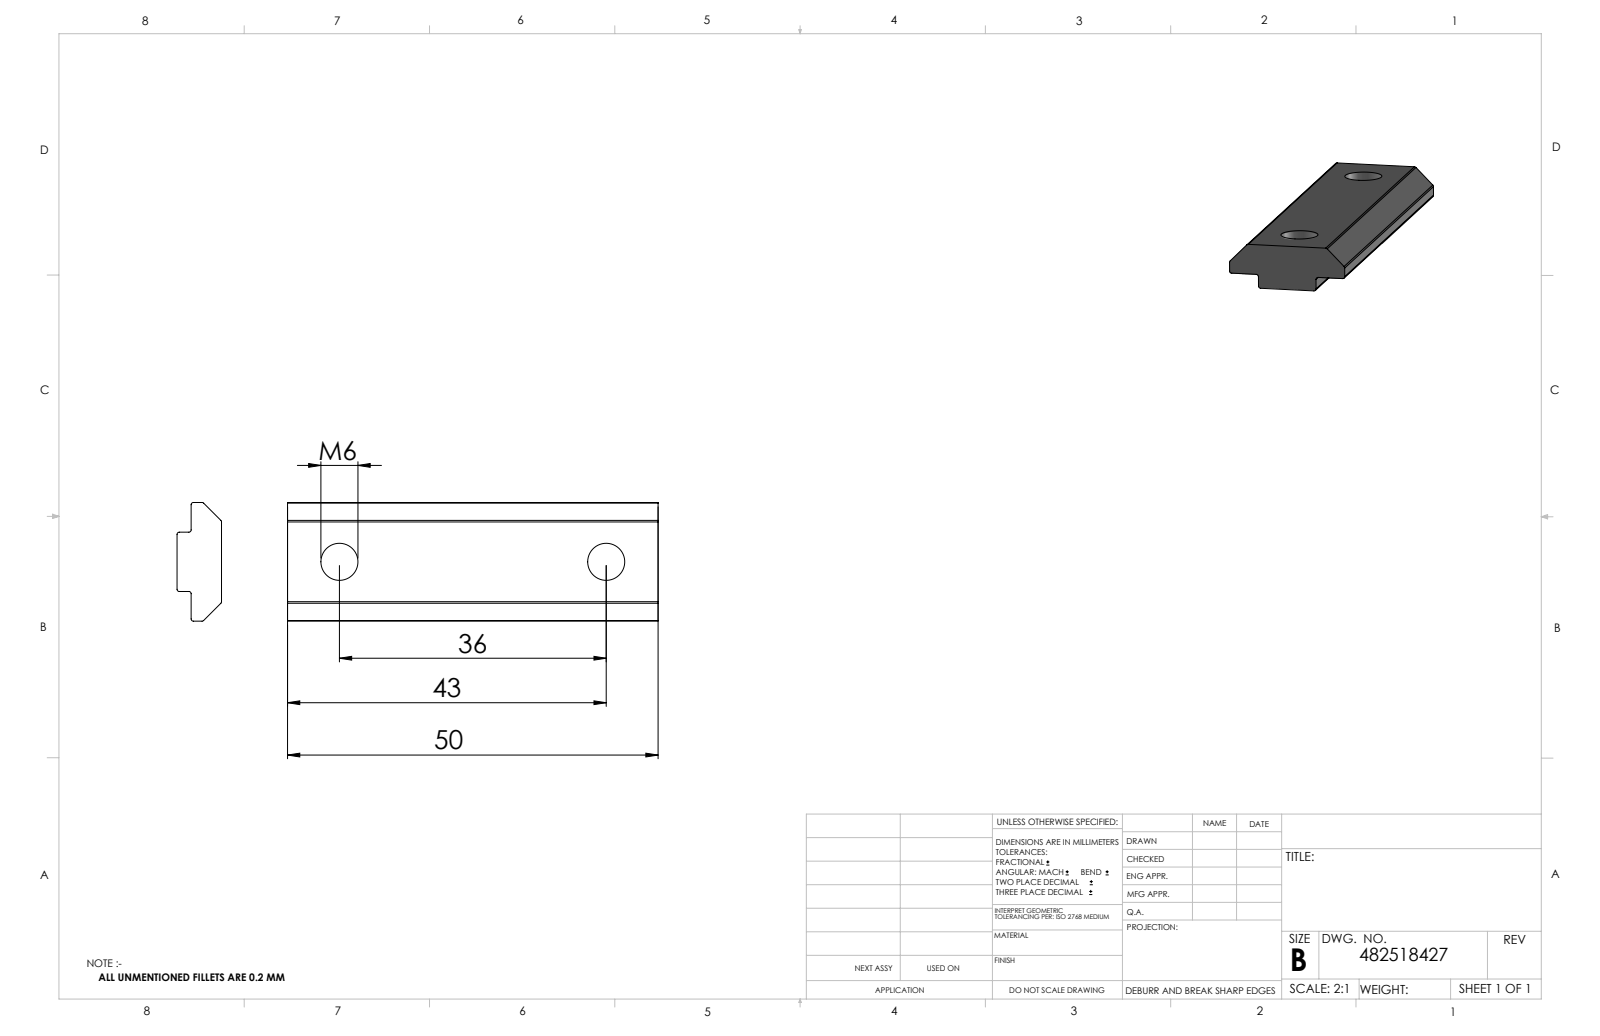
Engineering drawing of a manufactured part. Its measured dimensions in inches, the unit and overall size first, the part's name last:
Units: inches
Overall size (bounding box): 1.969 × 0.63 × 0.433
Round holes (diameter × count): ⌀0.197 ×2
Round bosses / shafts (diameter × count): ⌀0.236 ×2
Partial cylindrical surfaces — rounded edges, fillets, slot ends (radius × count): R0.012 ×10
Main face-to-face distances: 0.161, 0.236, 0.075, 0.157, 0.472, 1.969, 0.315, 0.197, 0.63, 0.039
Hole centre spacings: 1.417
Volume: 0.237 in³ · Surface area: 4.627 in²
Bodies: 3 solids, 264 faces (40 planar, 50 cylindrical, 174 other)
Part name (STEP PRODUCT): 482518427_c_1; 096010s04_Standard; 4din913m610_Standard
STEP written by: SolidWorks 2014 (CONFIG_CONTROL_DESIGN)
